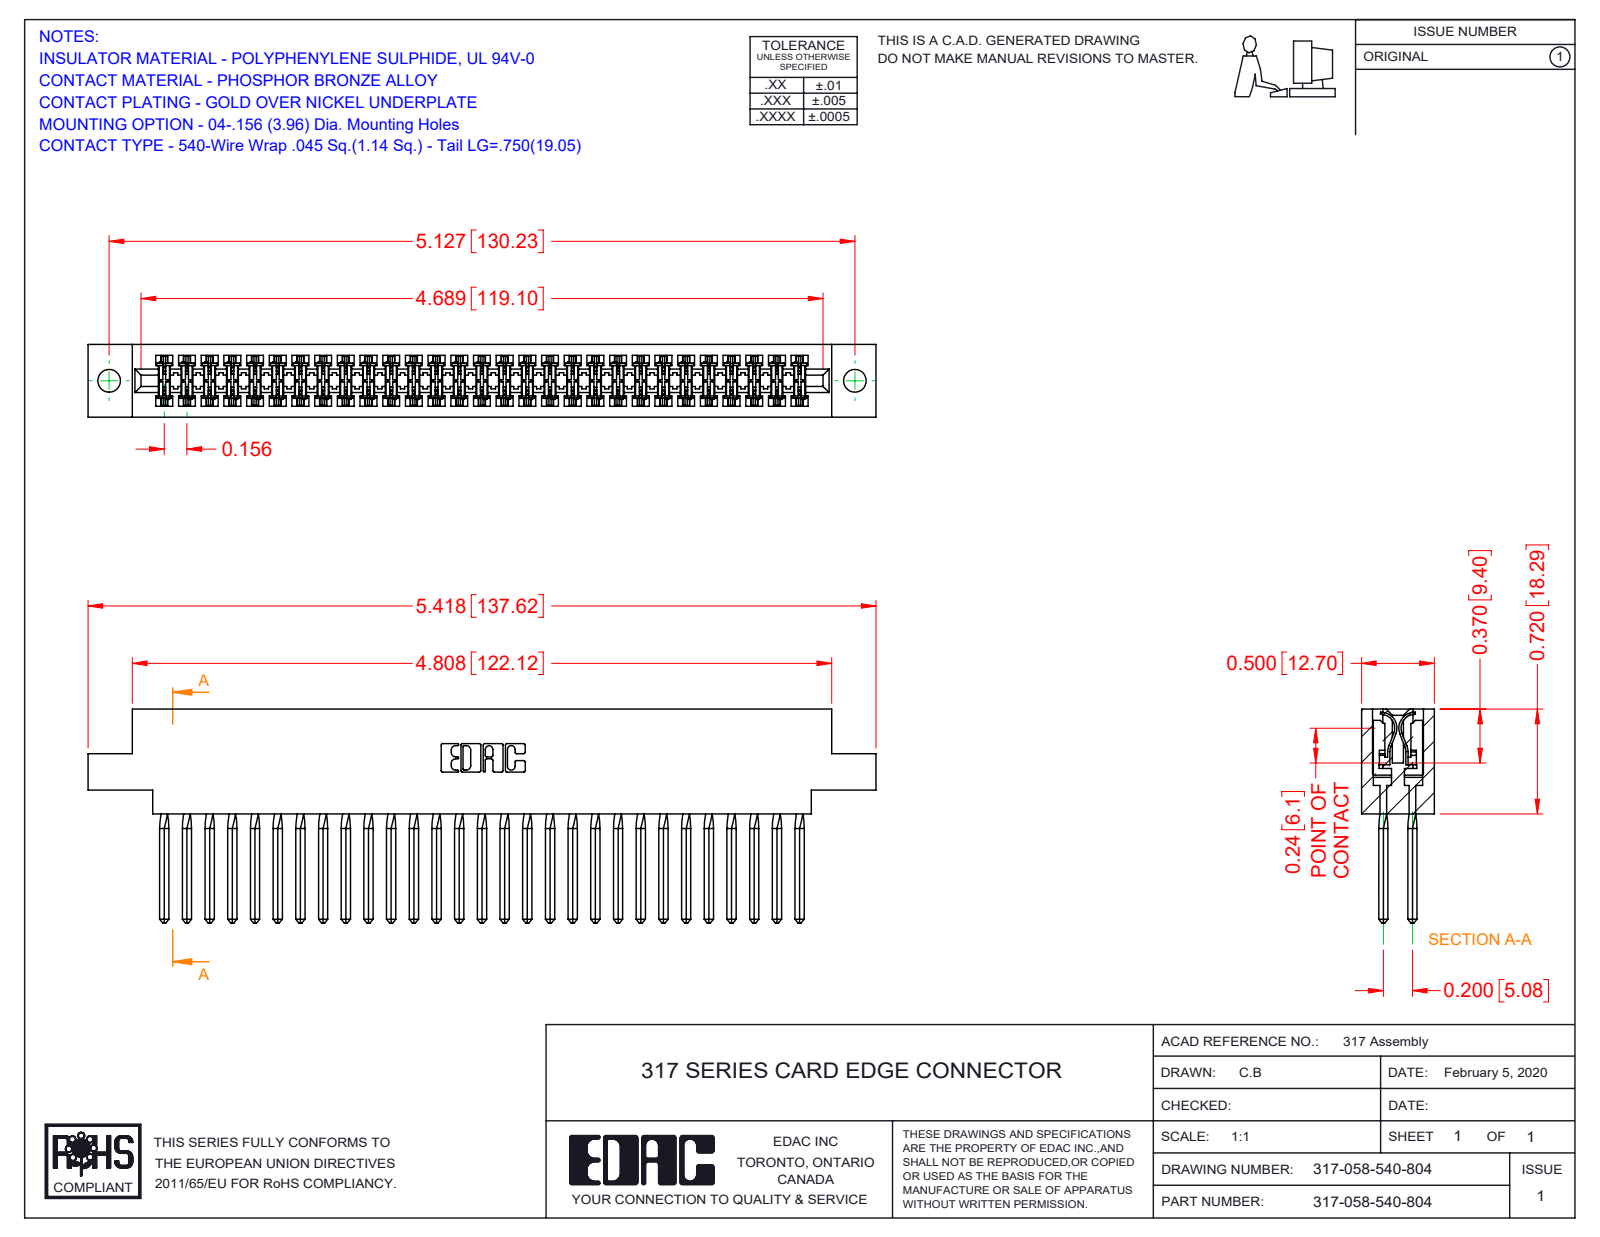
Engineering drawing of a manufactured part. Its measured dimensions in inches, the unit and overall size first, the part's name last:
Units: inches
Overall size (bounding box): 5.418 × 1.47 × 0.5
Round holes (diameter × count): ⌀0.156 ×2
Partial cylindrical surfaces — rounded edges, fillets, slot ends (radius × count): R0.015 ×116, R0.01 ×22, R0.007 ×6, R0.031 ×6, R0.026 ×3, R0.095 ×2, R0.1 ×2, R0.11 ×2
Main face-to-face distances: 0.5, 0.075, 0.425, 0.35, 0.11, 0.195, 0.094, 0.2, 0.72, 0.115
Hole centre spacings: 5.127
Volume: 1.377 in³ · Surface area: 51.12 in²
Bodies: 59 solids, 5264 faces (4292 planar, 740 cylindrical, 232 other)
Part name (STEP PRODUCT): 317 Part_.156 Dia - TH; 317-290-001_540; 317-058-540-804
STEP written by: SolidWorks 2016 (CONFIG_CONTROL_DESIGN)
